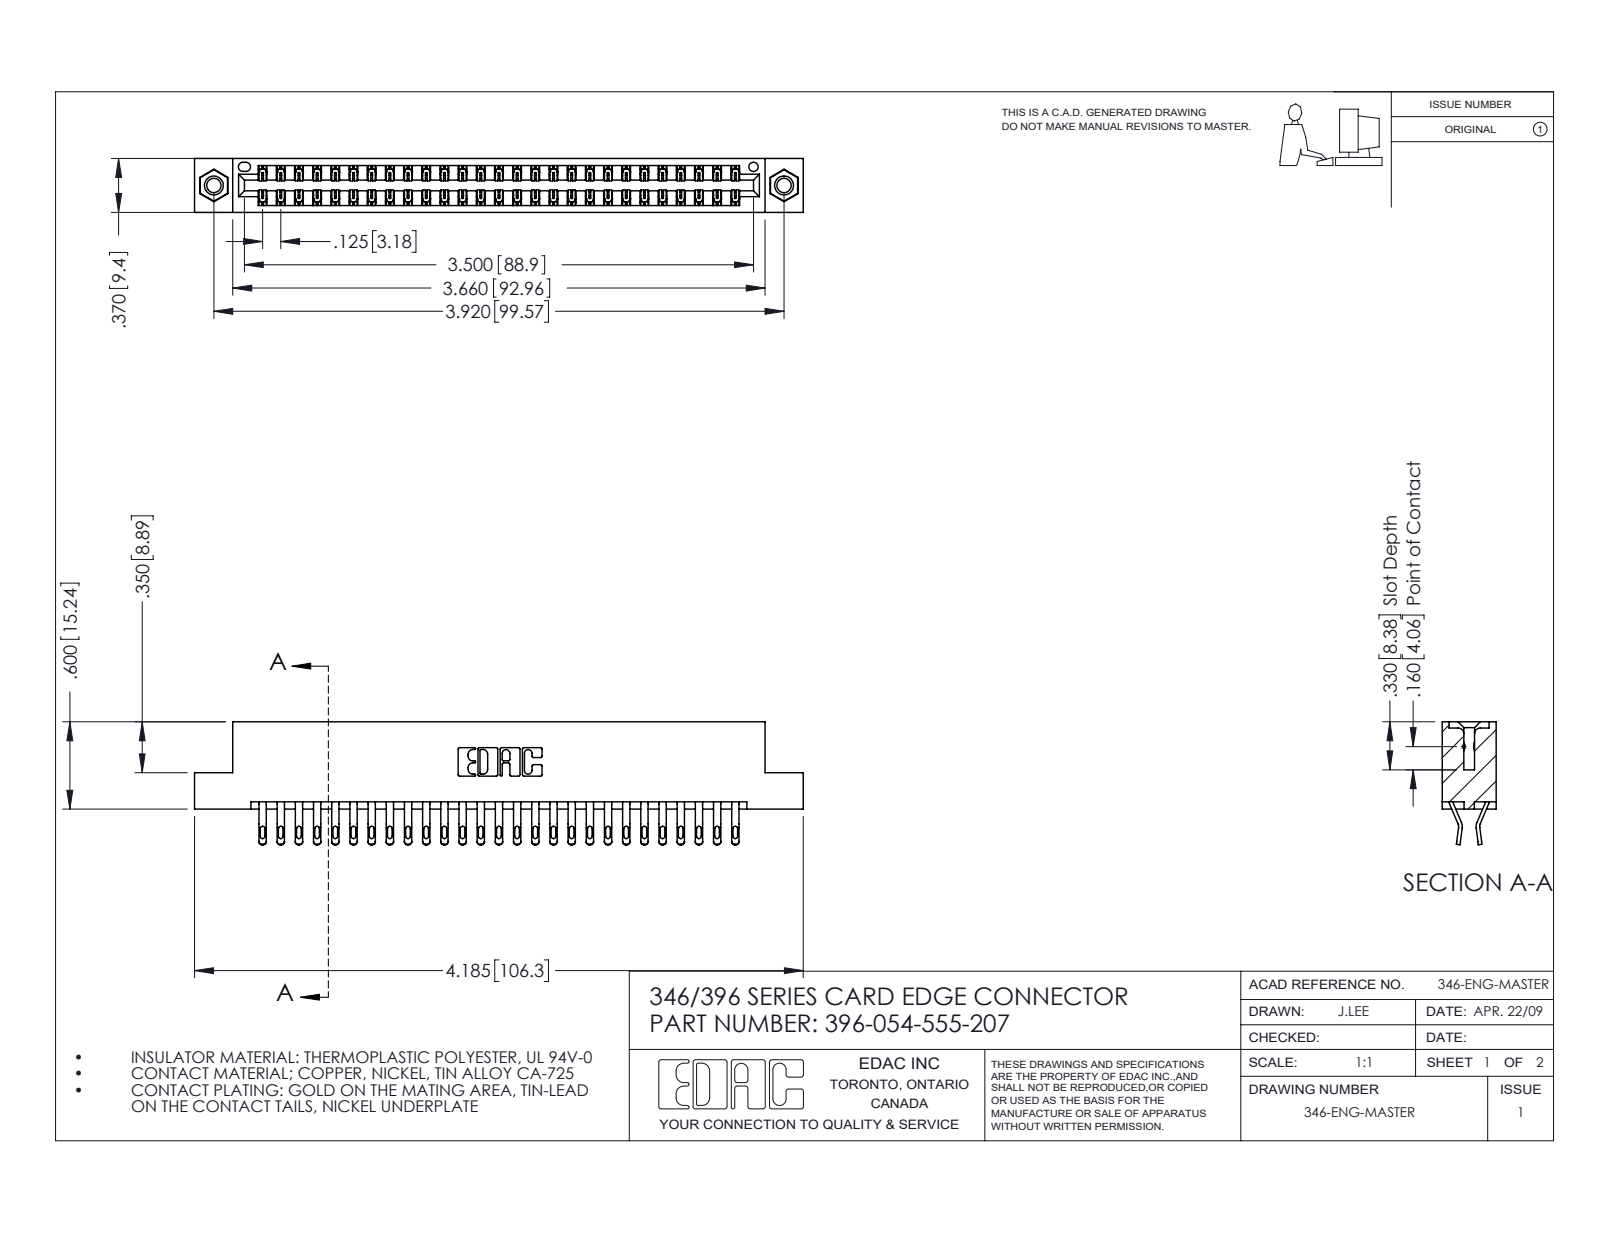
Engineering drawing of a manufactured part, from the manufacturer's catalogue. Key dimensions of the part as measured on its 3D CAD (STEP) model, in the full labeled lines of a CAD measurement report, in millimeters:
Part name (STEP PRODUCT): 396-054-555-207; 346 Part_Flush Mounting Lugs - 0.156 Dia-TI; 345-292-001_555 Tail; 345-250-001_345-250-005-103
STEP written by: SolidWorks 2016 (CONFIG_CONTROL_DESIGN)
Units: millimetres
Bodies: 57 solids, 3314 faces (1890 planar, 1408 cylindrical, 16 other)
Overall size (bounding box): 106.3 × 21.5 × 9.4
Volume: 10 400 mm³ · Surface area: 14 640 mm²
Round holes (diameter × count): ⌀2.5 ×2, ⌀3.2 ×2, ⌀4 ×2, ⌀1.6 ×1
Round bosses / shafts (diameter × count): ⌀3.9 ×2
Partial cylindrical surfaces — rounded edges, fillets, slot ends (radius × count): R0.4 ×108, R0.5 ×108, R0.2 ×81, R0.3 ×22, R0.2 ×6, R0.8 ×6, R0.7 ×3, R0.3 ×2
Main face-to-face distances: 1.2, 8.2, 9.4, 6.4, 0.6, 1.8, 7.6, 7, 3.8, 5.6
Hole centre spacings: 6.2, 94.3, 99.6
